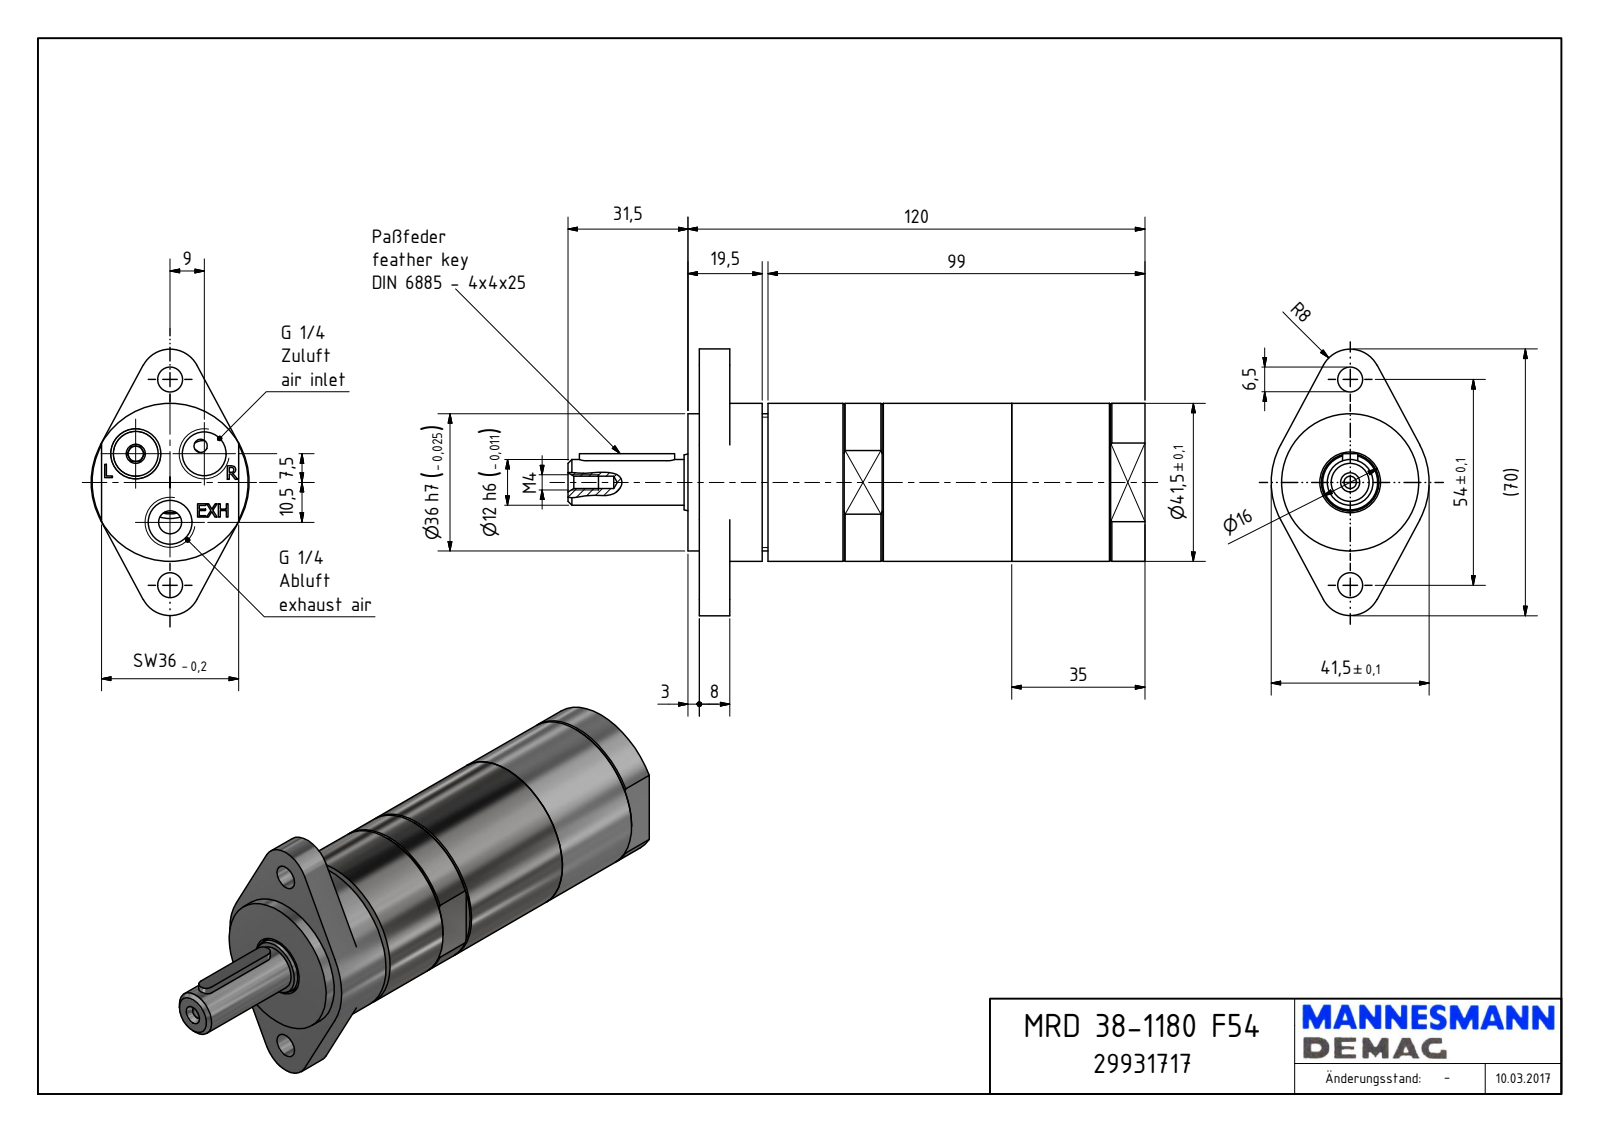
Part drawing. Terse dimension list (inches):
name: MRD 38-1180 F54_29931717
written by: Autodesk Inventor 2018 (AUTOMOTIVE_DESIGN)
unit: in
bodies: 1 solid, 153 faces (103 planar, 24 cylindrical, 26 other)
size: 5.965 × 2.756 × 1.634
volume: 10.02 in³; area: 36.57 in²
holes: 3× ⌀0.451, 2× ⌀0.256, 1× ⌀0.128, 1× ⌀0.157, 1× ⌀0.63
bosses: 1× ⌀1.634, 1× ⌀1.417, 1× ⌀0.589, 1× ⌀0.472
rounds: 2× R0.079, 2× R0.315
face distances: 4.606, 0.118, 4.724, 0.433, 0.315, 4.291, 0.394, 0.039, 3.898, 0.827
hole spacings: 0.461, 0.792, 0.846, 1.063, 1.404, 0.413, 0.65, 0.709
